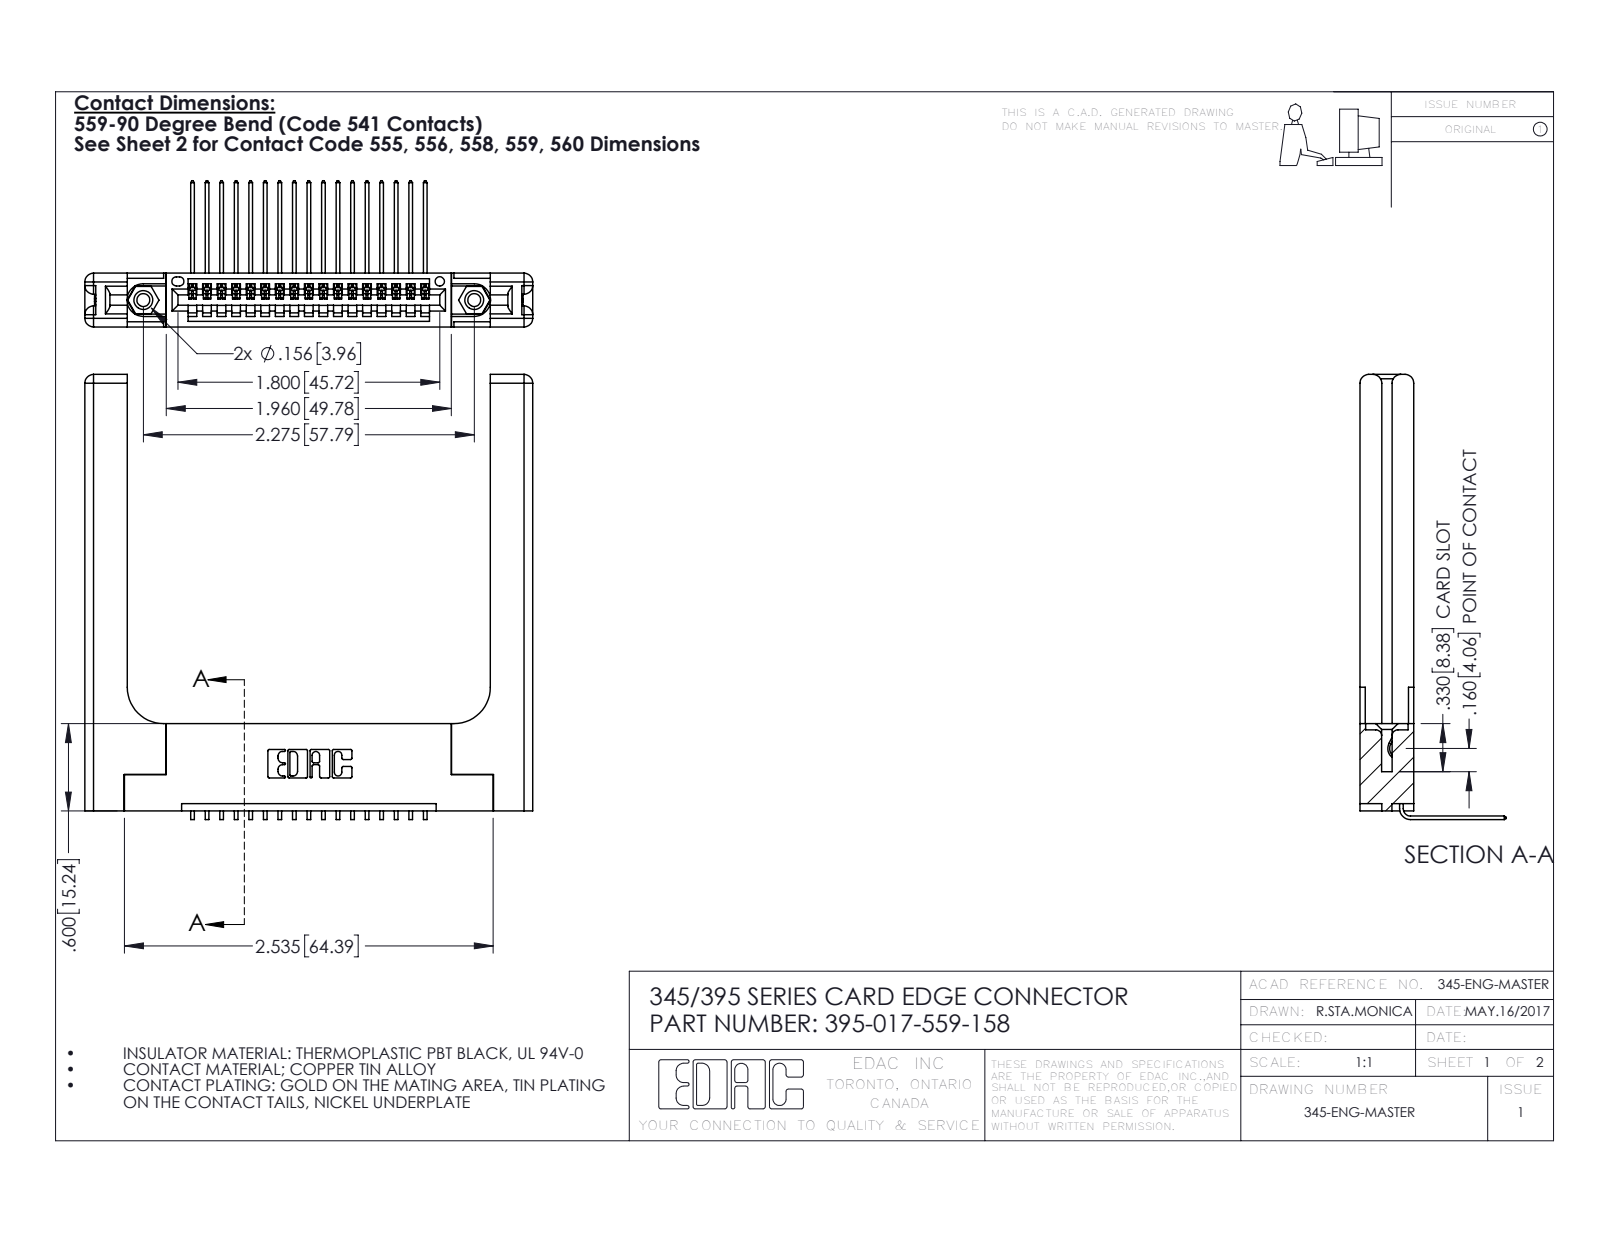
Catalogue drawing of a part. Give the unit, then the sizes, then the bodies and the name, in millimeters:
Units: millimetres
Overall size (bounding box): 78.2 × 77.7 × 25.5
Round holes (diameter × count): ⌀2.3 ×2, ⌀3.2 ×2, ⌀4 ×2, ⌀1.6 ×1
Round bosses / shafts (diameter × count): ⌀3.9 ×2
Partial cylindrical surfaces — rounded edges, fillets, slot ends (radius × count): R0.2 ×34, R0.3 ×22, R1.5 ×16, R0.2 ×6, R0.8 ×6, R0.7 ×3, R0.8 ×2, R0.8 ×2
Main face-to-face distances: 9.4, 1.8, 7.6, 3.8, 3.8, 2, 5.6, 5.1, 2.5, 6.9
Hole centre spacings: 6.9, 51.8, 57.8
Volume: 15 800 mm³ · Surface area: 14 970 mm²
Bodies: 22 solids, 1402 faces (942 planar, 400 cylindrical, 60 other)
Part name (STEP PRODUCT): 345-220-058_345-220-058; 395-017-559-158; 345-292-001_558 559 Tail - 1; 345 Part_Flush Mounting Lugs - 0.156 Dia-TH (+1 more)
STEP written by: SolidWorks 2016 (CONFIG_CONTROL_DESIGN)
